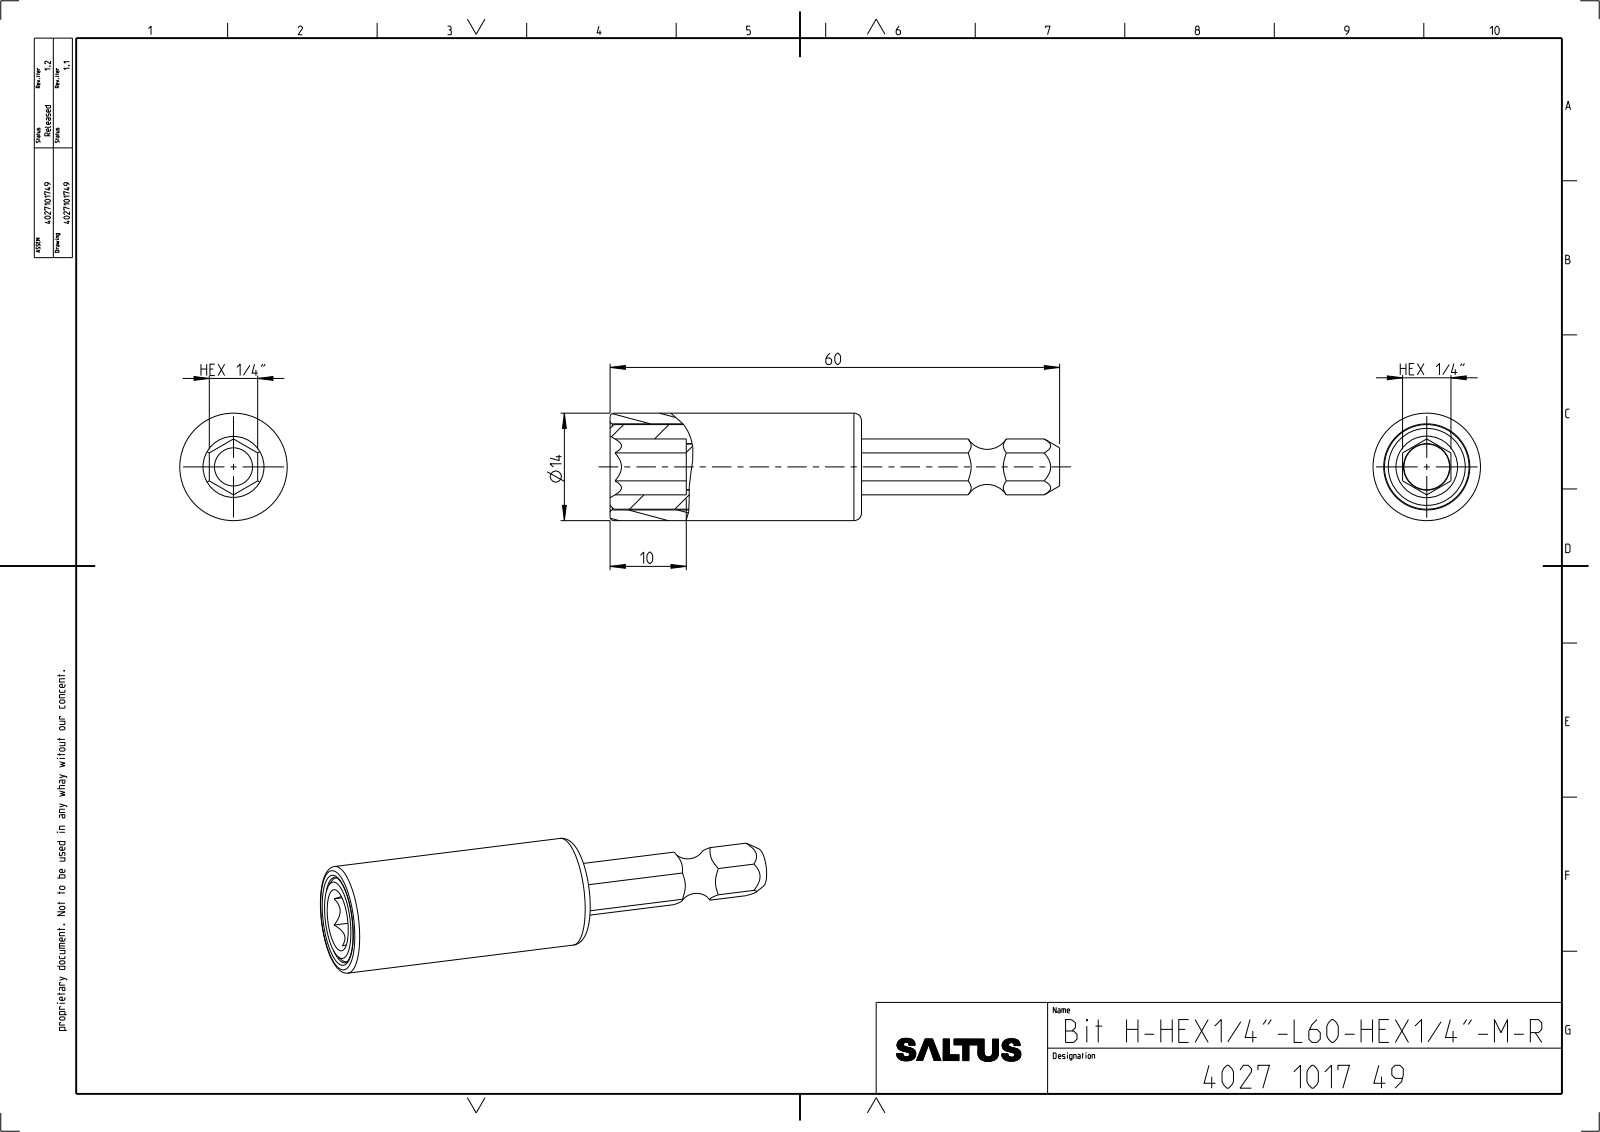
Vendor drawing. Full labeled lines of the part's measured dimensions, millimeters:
Part name (STEP PRODUCT): 4027911195; 4027299498; 4027101749_ASM
STEP written by: CREO PARAMETRIC BY PTC INC, 2022414 (CONFIG_CONTROL_DESIGN)
Units: millimetres
Bodies: 2 solids, 75 faces (27 planar, 22 cylindrical, 26 other)
Overall size (bounding box): 59 × 14.1 × 14.1
Volume: 5 403 mm³ · Surface area: 5 124 mm²
Round holes (diameter × count): ⌀6.1 ×1, ⌀8 ×1, ⌀11.3 ×1
Round bosses / shafts (diameter × count): ⌀14.1 ×1, ⌀11.1 ×1, ⌀6 ×1
Partial cylindrical surfaces — rounded edges, fillets, slot ends (radius × count): R0.5 ×6
Main face-to-face distances: 6.34, 33, 23, 10, 2.5, 20.5, 30.5, 2, 0.5, 21
